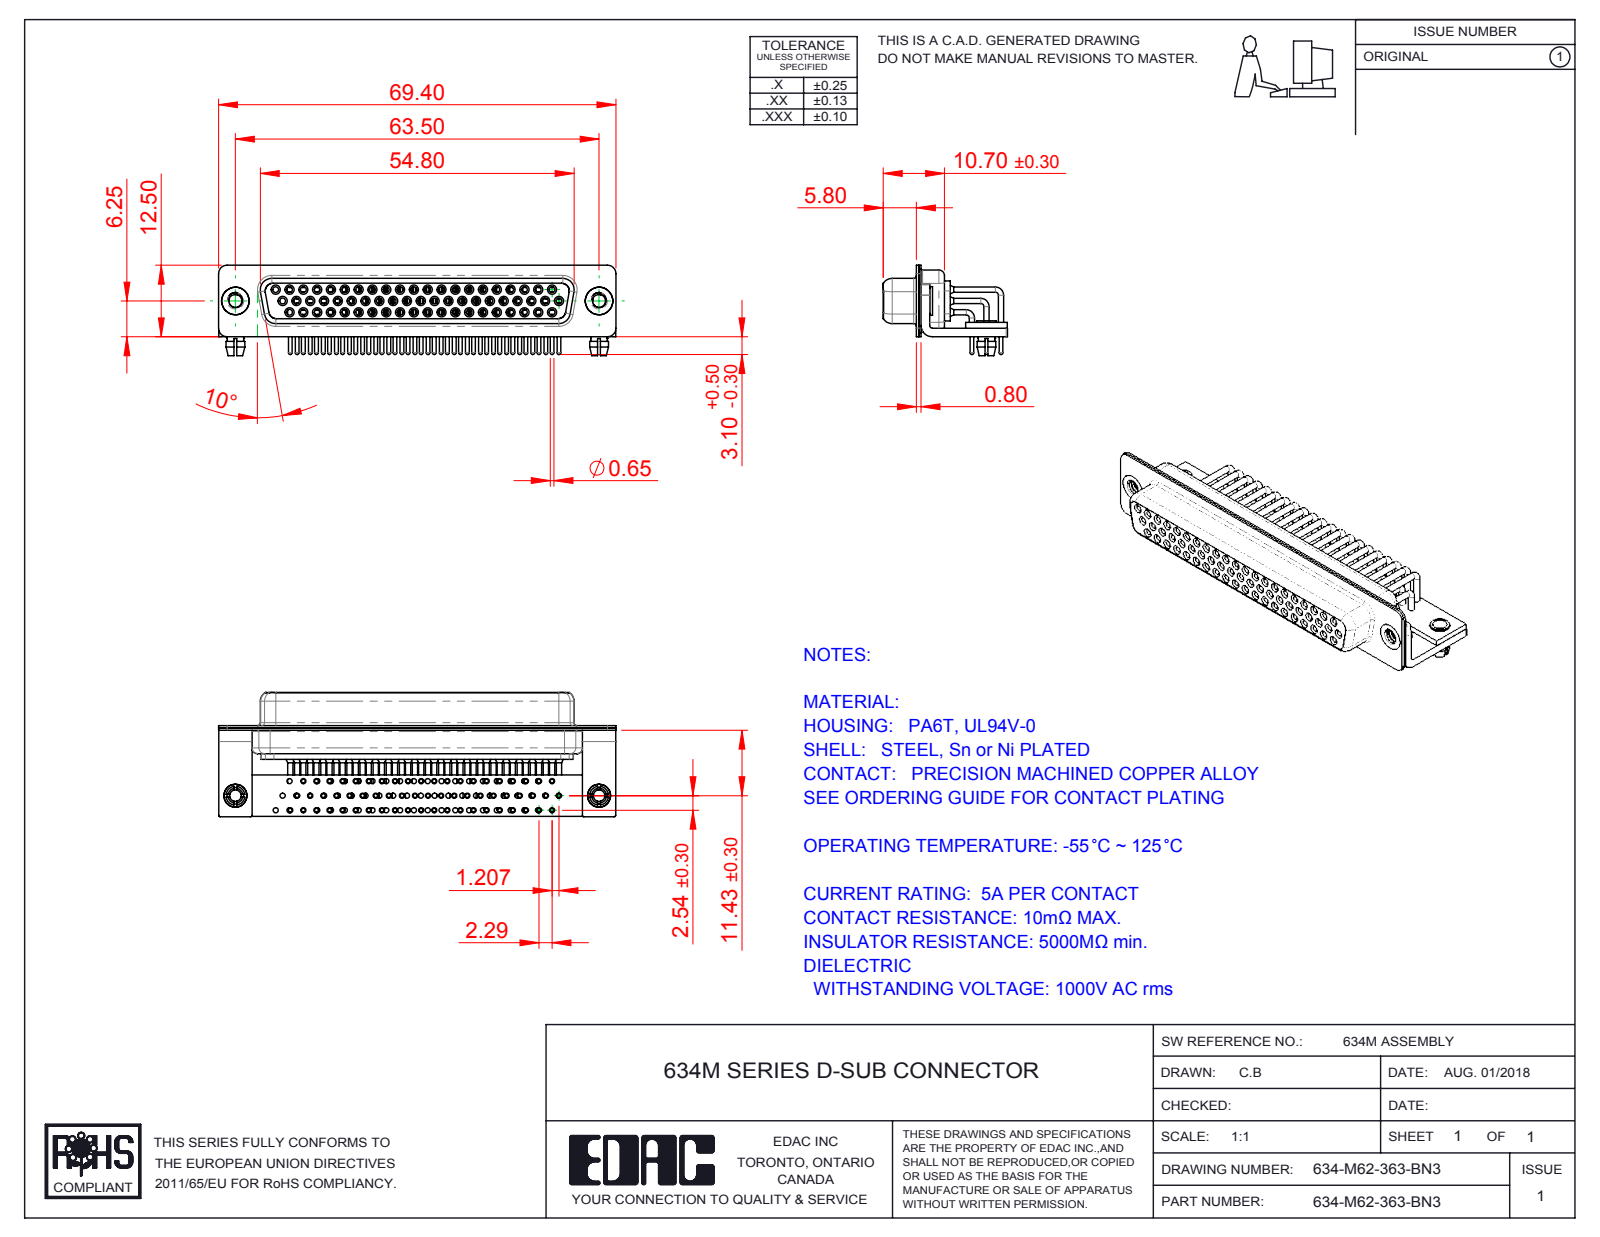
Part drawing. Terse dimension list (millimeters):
name: 634-M62-363-BN3; 634M Contact Row 1; 634M Board Lock; 634M Housing_62 Contacts (+7 more)
written by: SolidWorks 2016 (CONFIG_CONTROL_DESIGN)
unit: mm
bodies: 72 solids, 3831 faces (1071 planar, 1741 cylindrical, 1019 other)
size: 69.4 × 21.7 × 15.8
volume: 6 178 mm³; area: 19 963 mm²
holes: 64× ⌀2, 62× ⌀0.9, 62× ⌀1, 62× ⌀1.1, 62× ⌀1.7, 62× ⌀1.8, 2× ⌀2.26, 2× ⌀2.5, 2× ⌀3.2, 2× ⌀4, 2× ⌀4.8
bosses: 118× ⌀0.9, 62× ⌀1.6, 62× ⌀1.5, 62× ⌀0.65, 56× ⌀2, 2× ⌀5, 2× ⌀4.9, 2× ⌀4
rounds: 16× R0.25, 16× R1.5, 13× R2, 8× R1.35, 8× R1.6, 5× R0.5, 4× R0.6, 4× R0.65
face distances: 0.4, 2.3, 1, 1.9, 1.45, 8.95, 8.5, 0.85, 0.8, 9.35
hole spacings: 7.24, 2.41, 9.65, 4.83, 14.48, 16.89, 2.81, 2.32
